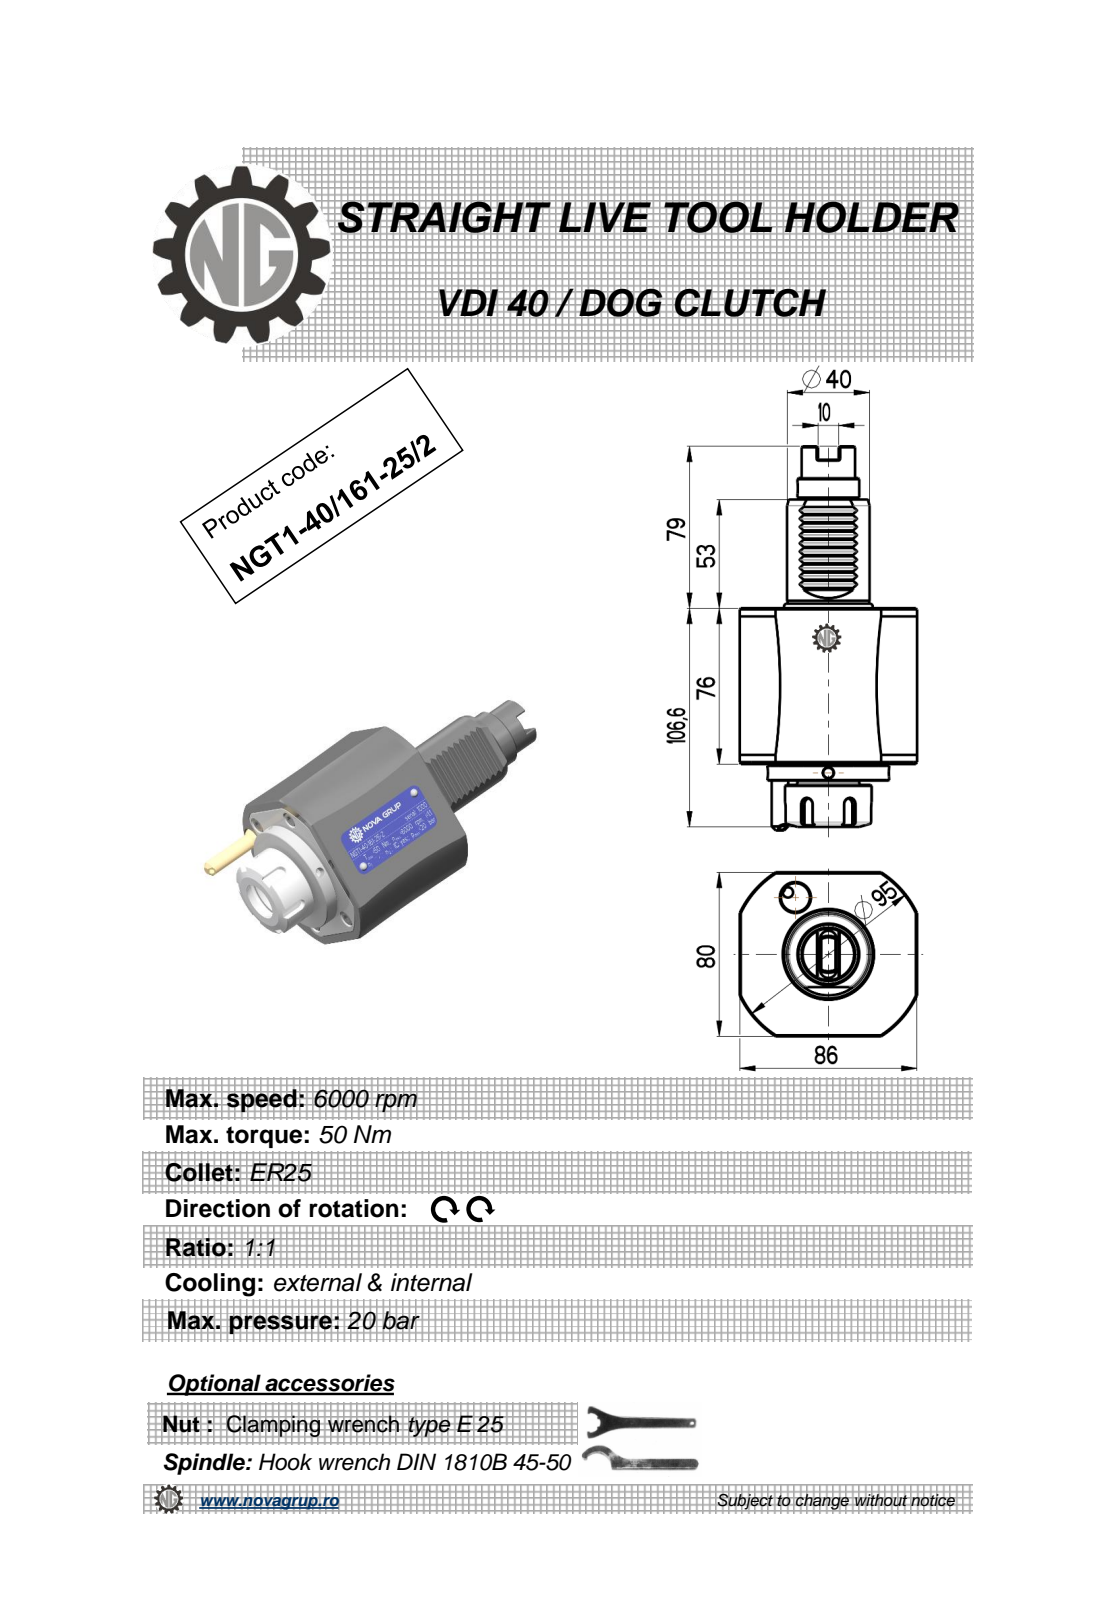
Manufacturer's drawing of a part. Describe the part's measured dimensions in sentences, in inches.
The part is named "NGT1_40_161_25_1". Its 3-D file was written by "PRO/ENGINEER BY PARAMETRIC TECHNOLOGY CORPORATION, 2010280 (CONFIG_CONTROL_DESIGN)". It is 1 solid with 310 faces: 113 planar, 76 cylindrical and 121 other. Overall it measures 7.376 by 3.386 by 3.15 inches. Its volume is 36.6 cubic inches and its surface area 83.88 square inches. Round holes: 3 of diameter 0.197, 1 of diameter 0.118, 1 of diameter 0.165. Round bosses or shafts: 1 of diameter 2.323, 1 of diameter 1.89, 1 of diameter 1.654, 1 of diameter 1.575, 1 of diameter 1.299, 1 of diameter 1.181, 1 of diameter 1.024, 1 of diameter 0.315. Partial cylindrical surfaces (rounded edges, fillets, slot ends): 10 of radius 0.012, 6 of radius 0.009, 6 of radius 0.01, 5 of radius 0.118, 2 of radius 0.02, 2 of radius 0.157, 1 of radius 0.354, 1 of radius 1.87. The main face-to-face distances are 2.992, 3.15, 3.386, 3.307, 0.315, 0.02, 0.295, 0.111, 3.012, 5.098. The hole center spacings are 5.463.
